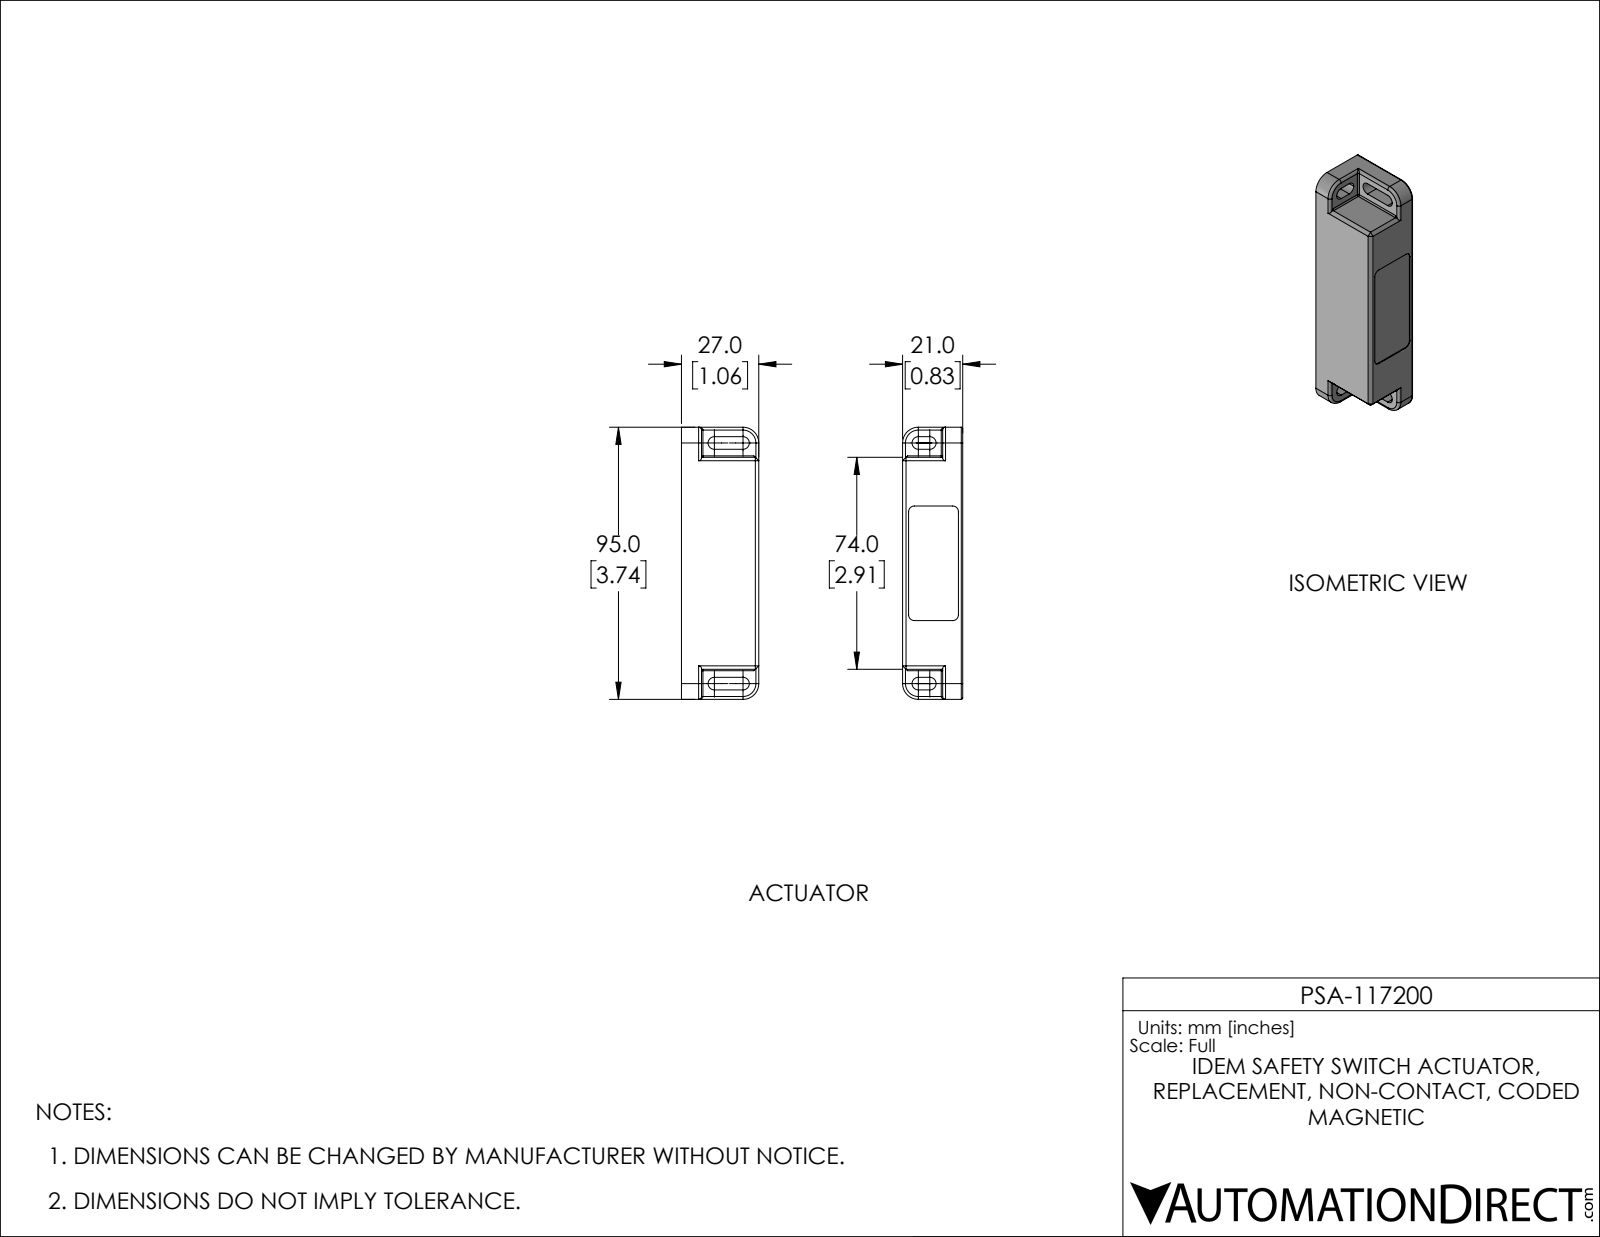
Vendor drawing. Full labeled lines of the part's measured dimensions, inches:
Part name (STEP PRODUCT): 117-PSA-Actuator
STEP written by: SolidWorks 2019 (AUTOMOTIVE_DESIGN)
Units: inches
Bodies: 1 solid, 405 faces (214 planar, 98 cylindrical, 93 other)
Overall size (bounding box): 3.74 × 1.063 × 0.827
Volume: 1.161 in³ · Surface area: 27.16 in²
Round bosses / shafts (diameter × count): ⌀0.197 ×1, ⌀0.079 ×1
Partial cylindrical surfaces — rounded edges, fillets, slot ends (radius × count): R0.02 ×37, R0.012 ×8, R0.087 ×8, R0.039 ×6, R0.008 ×4, R0.079 ×4, R0.217 ×4
Main face-to-face distances: 0.079, 0.748, 0.827, 0.669, 0.976, 0.063, 0.913, 0.992, 1.055, 0.067
